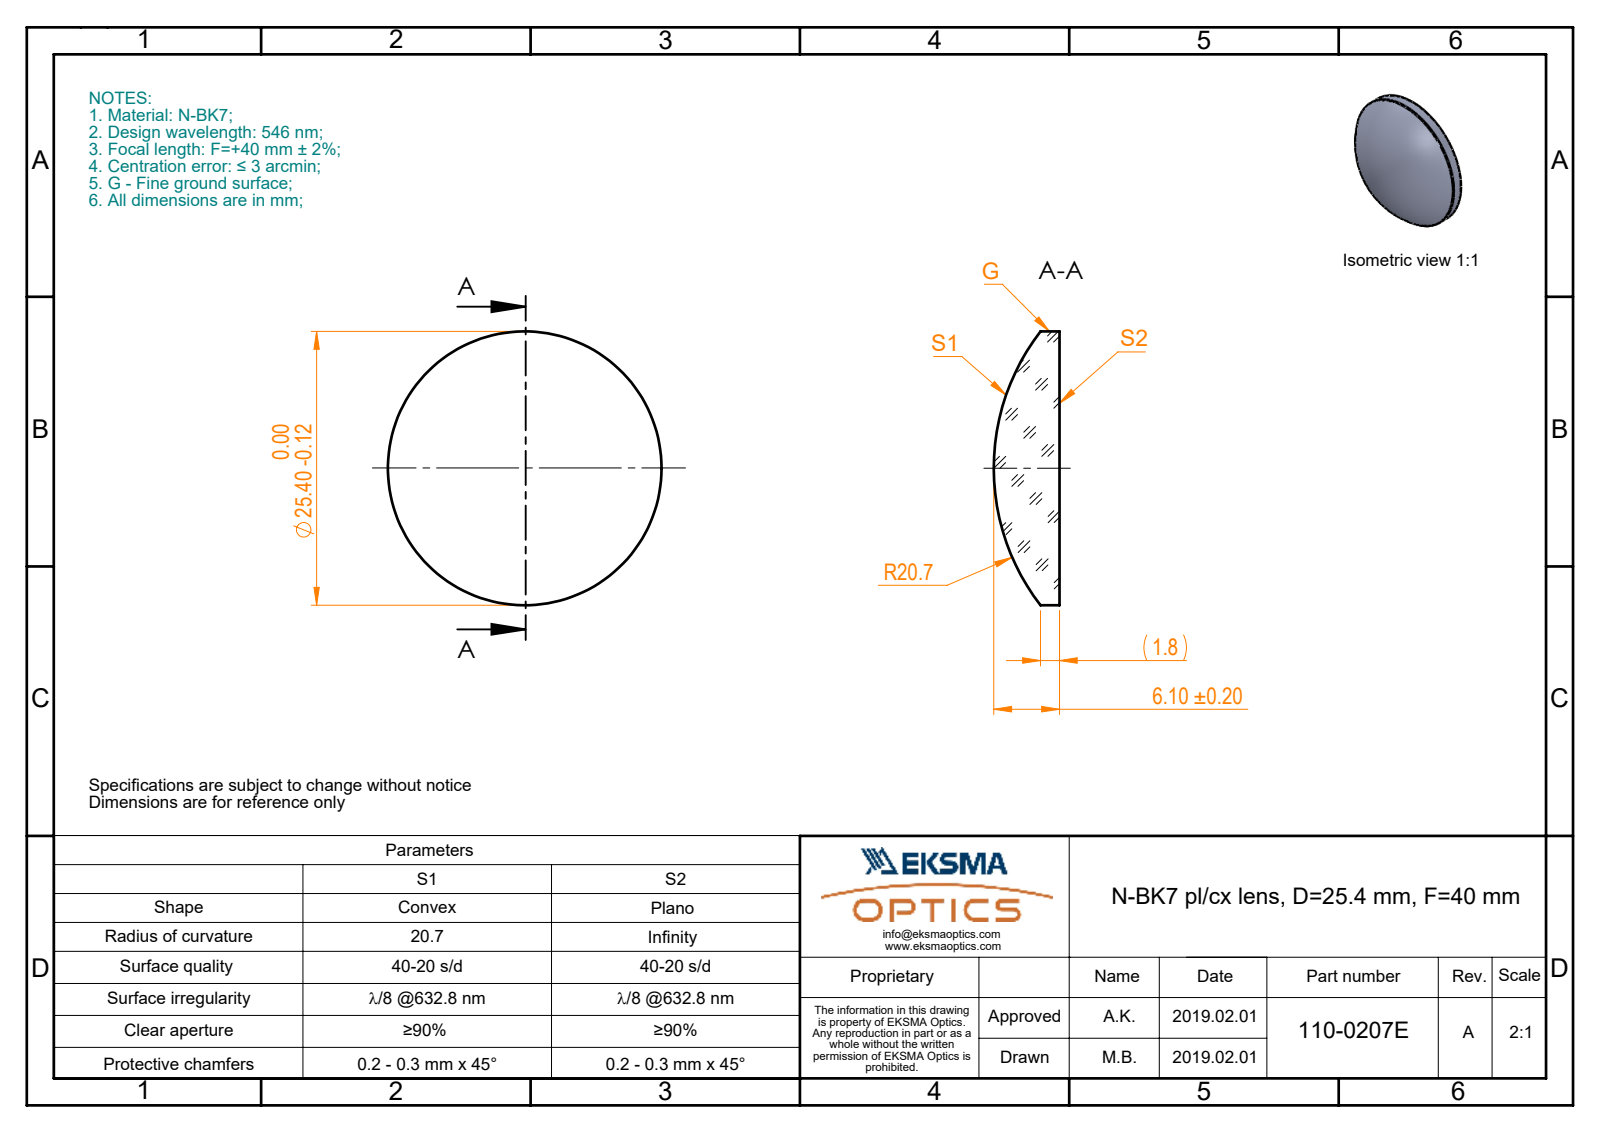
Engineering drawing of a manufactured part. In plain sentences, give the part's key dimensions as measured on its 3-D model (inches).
The part is named "110-0207E BK7 pl-cx 25.4 F40". Its 3-D file was written by "SolidWorks 2017 (CONFIG_CONTROL_DESIGN)". It is 1 solid with 5 faces: 1 planar, 2 cylindrical and 2 other. Overall it measures 1 by 1 by 0.24 inches. Its volume is 0.124 cubic inches and its surface area 1.88 square inches. Round bosses or shafts: 1 of diameter 1.
